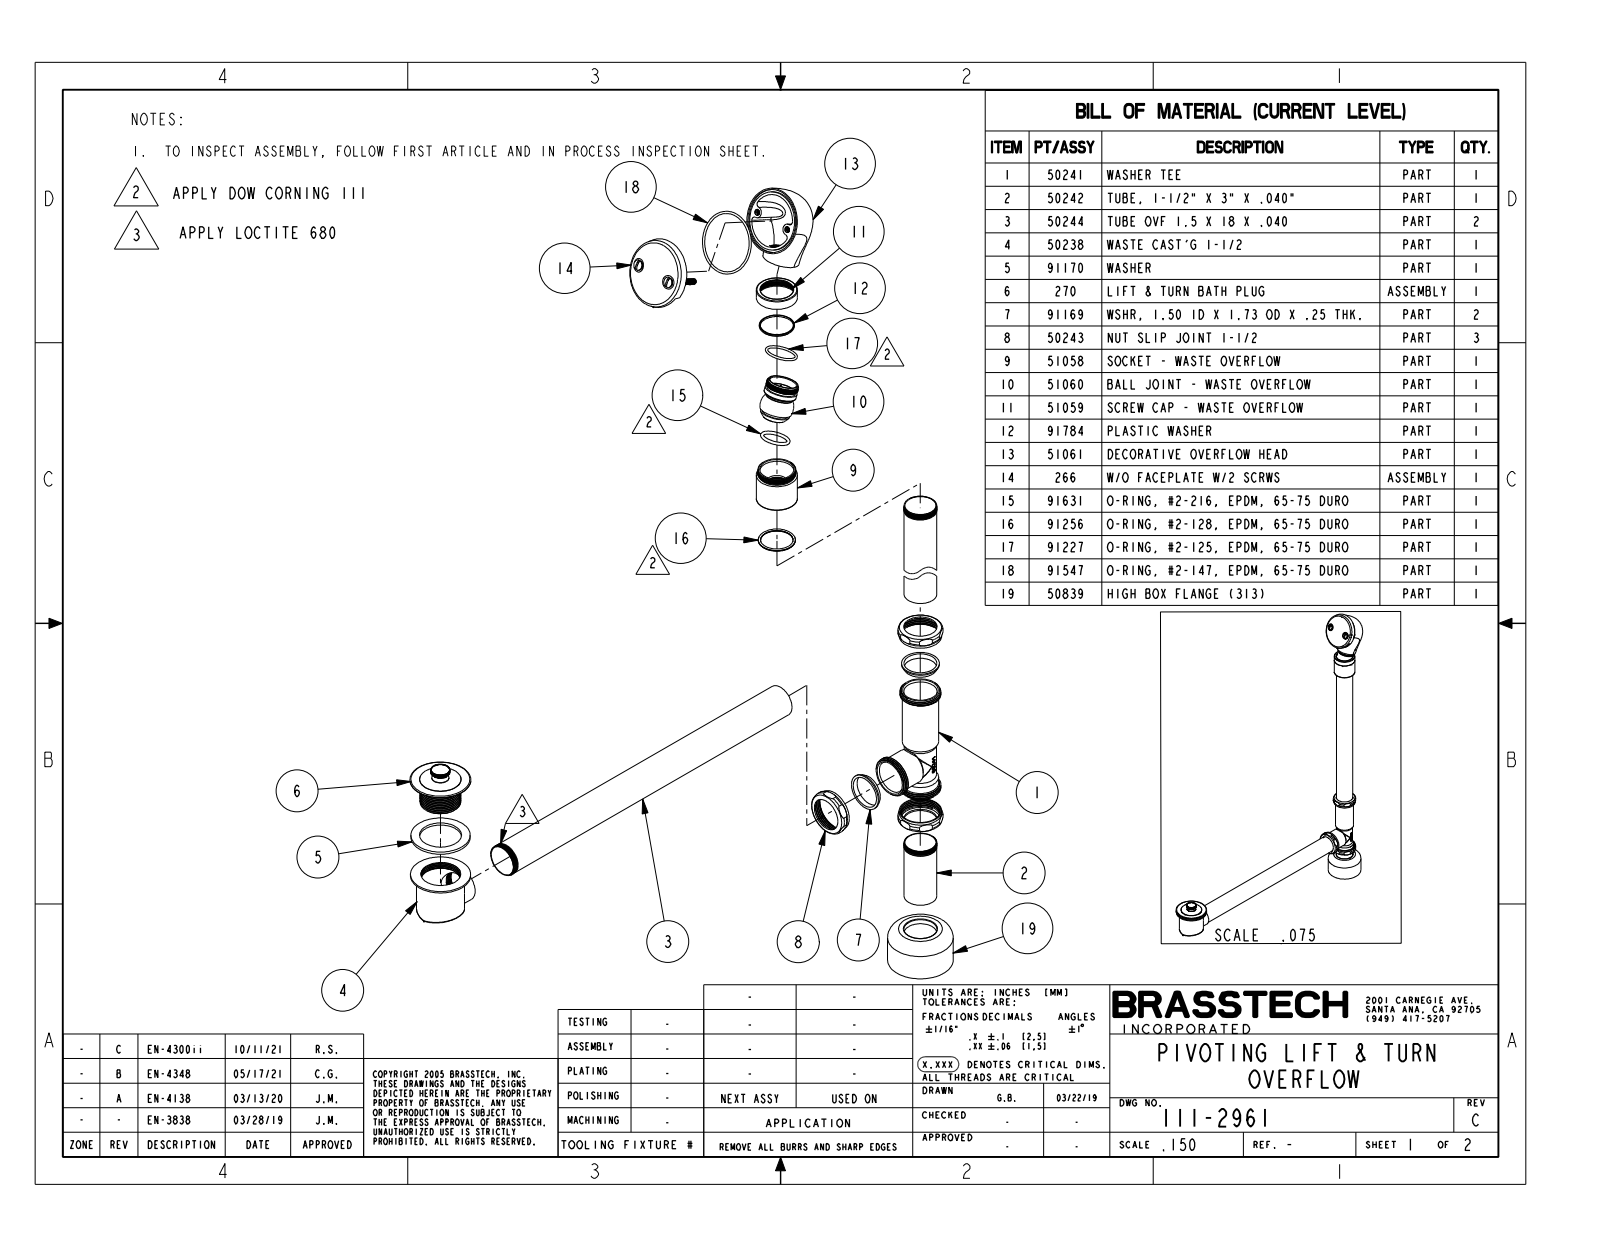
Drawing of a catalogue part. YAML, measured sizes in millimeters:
part_name: "50241; 50242; 50244; 50238 (+8 more)"
step_written_by: "CREO PARAMETRIC BY PTC INC, 2018400 (AUTOMOTIVE_DESIGN)"
units: millimeters
bodies: {solids: 30, faces: 1679, planar: 376, cylindrical: 739, other: 564}
overall_size: [723.3, 585.5, 80.8]
volume: 403000
surface_area: 476300
round_holes:
  - {diameter: 38.6, count: 4}
  - {diameter: 45.3, count: 3}
  - {diameter: 4.9, count: 2}
  - {diameter: 6.9, count: 2}
  - {diameter: 36.1, count: 2}
  - {diameter: 3.3, count: 1}
  - {diameter: 5.4, count: 1}
  - {diameter: 10.5, count: 1}
  - {diameter: 12.1, count: 1}
  - {diameter: 16.5, count: 1}
  - {diameter: 24.1, count: 1}
  - {diameter: 25.4, count: 1}
round_bosses_or_shafts:
  - {diameter: 42.2, count: 3}
  - {diameter: 38.1, count: 3}
  - {diameter: 49.3, count: 2}
  - {diameter: 47.5, count: 2}
  - {diameter: 43.9, count: 2}
  - {diameter: 12.2, count: 2}
  - {diameter: 6.2, count: 2}
  - {diameter: 76.2, count: 1}
partial_cylinders:
  - {radius: 1, count: 5}
  - {radius: 6.4, count: 2}
  - {radius: 26.2, count: 2}
  - {radius: 1.4, count: 1}
  - {radius: 7.4, count: 1}
  - {radius: 10, count: 1}
  - {radius: 10.9, count: 1}
  - {radius: 18.3, count: 1}
face_to_face_distances: [3, 2, 50, 5.1, 86.5, 88.6, 91.6, 0.6, 86, 88]
hole_center_spacings: [24.6, 49.3, 24, 503.6]
